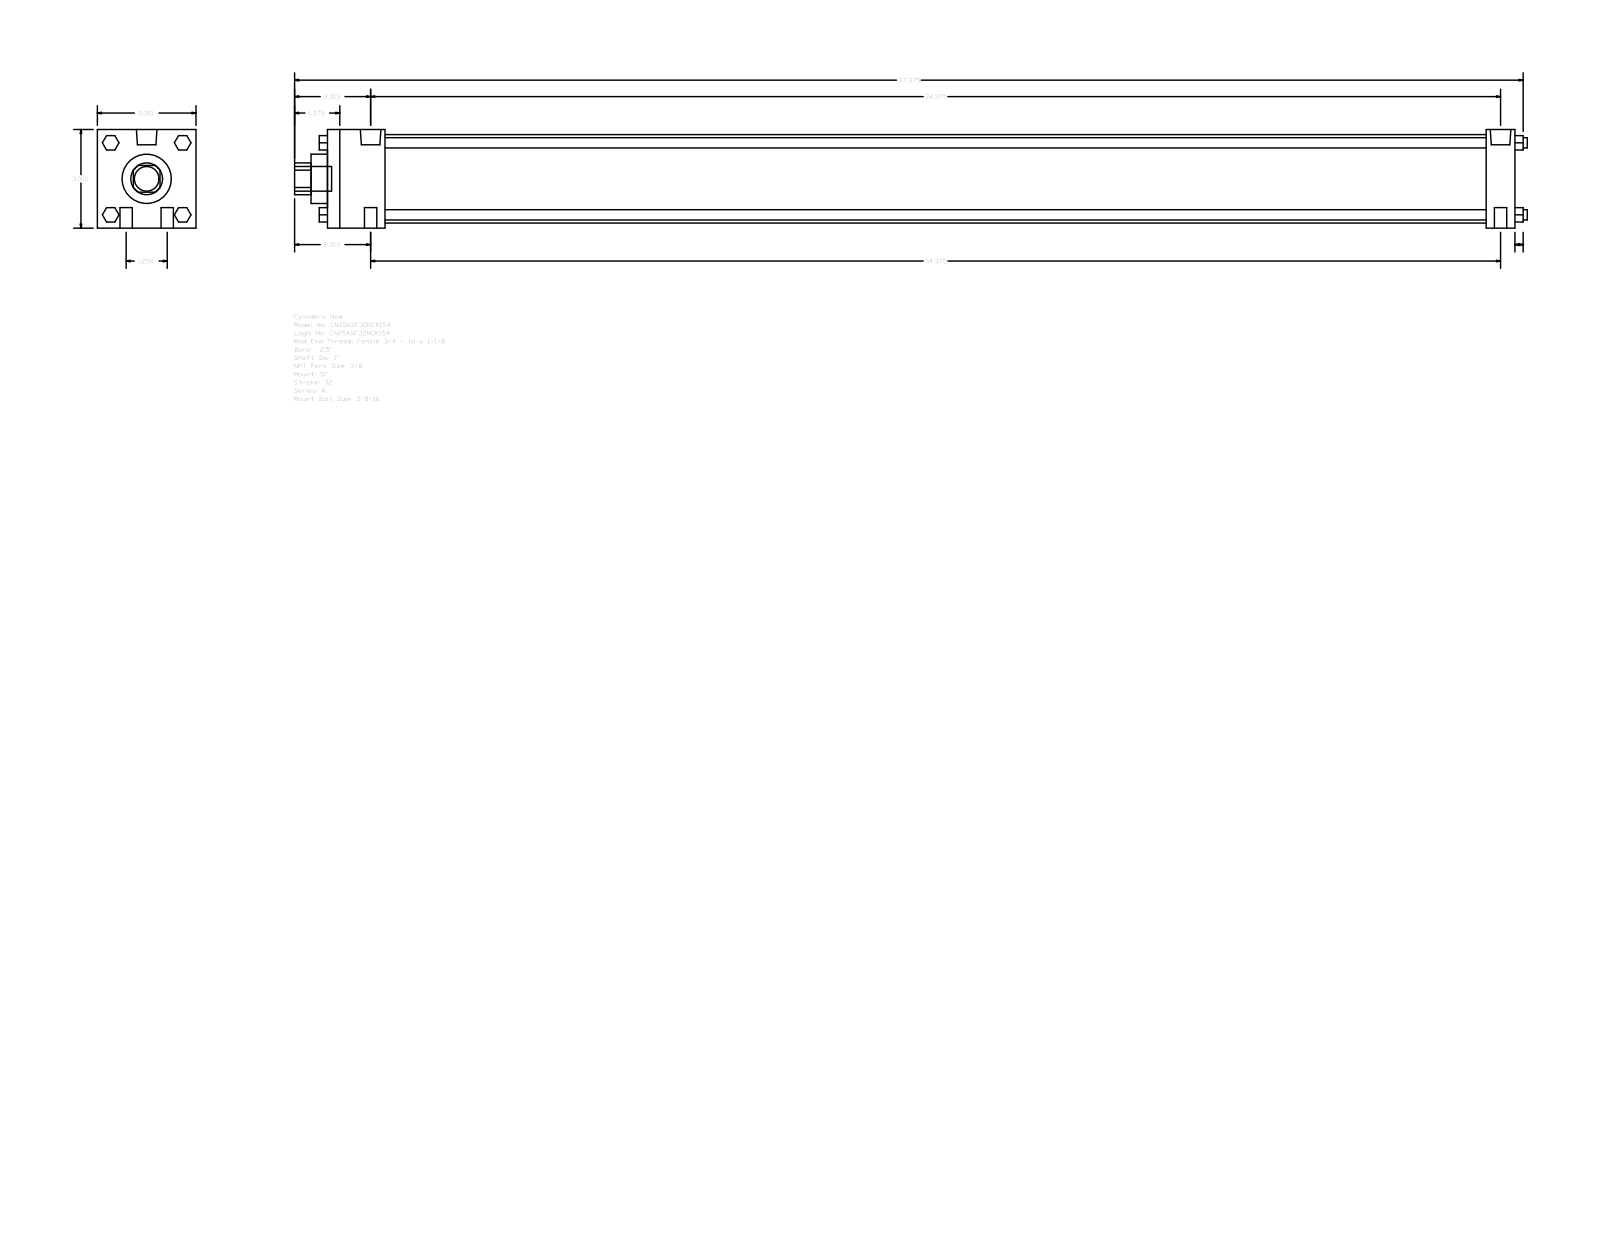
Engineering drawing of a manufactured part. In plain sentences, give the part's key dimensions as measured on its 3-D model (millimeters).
The part is named "A_SF__0250_1". Its 3-D file was written by "GSSL Pune (CONFIG_CONTROL_DESIGN)". It is 0 solids with 124 faces: 94 planar, 30 cylindrical and 0 other. Overall it measures 952.5 by 76.2 by 76.2 millimeters. Round holes: 1 of diameter 25.4, 1 of diameter 38.1, 1 of diameter 68.33. Round bosses or shafts: 4 of diameter 9.53, 4 of diameter 7.94, 2 of diameter 15.93, 2 of diameter 5.56, 1 of diameter 19.05. Partial cylindrical surfaces (rounded edges, fillets, slot ends): 1 of radius 12.29. The main face-to-face distances are 76.2, 917.58, 895.35, 22.23, 44.45, 850.9, 873.13, 12.7, 930.28, 6.35.
